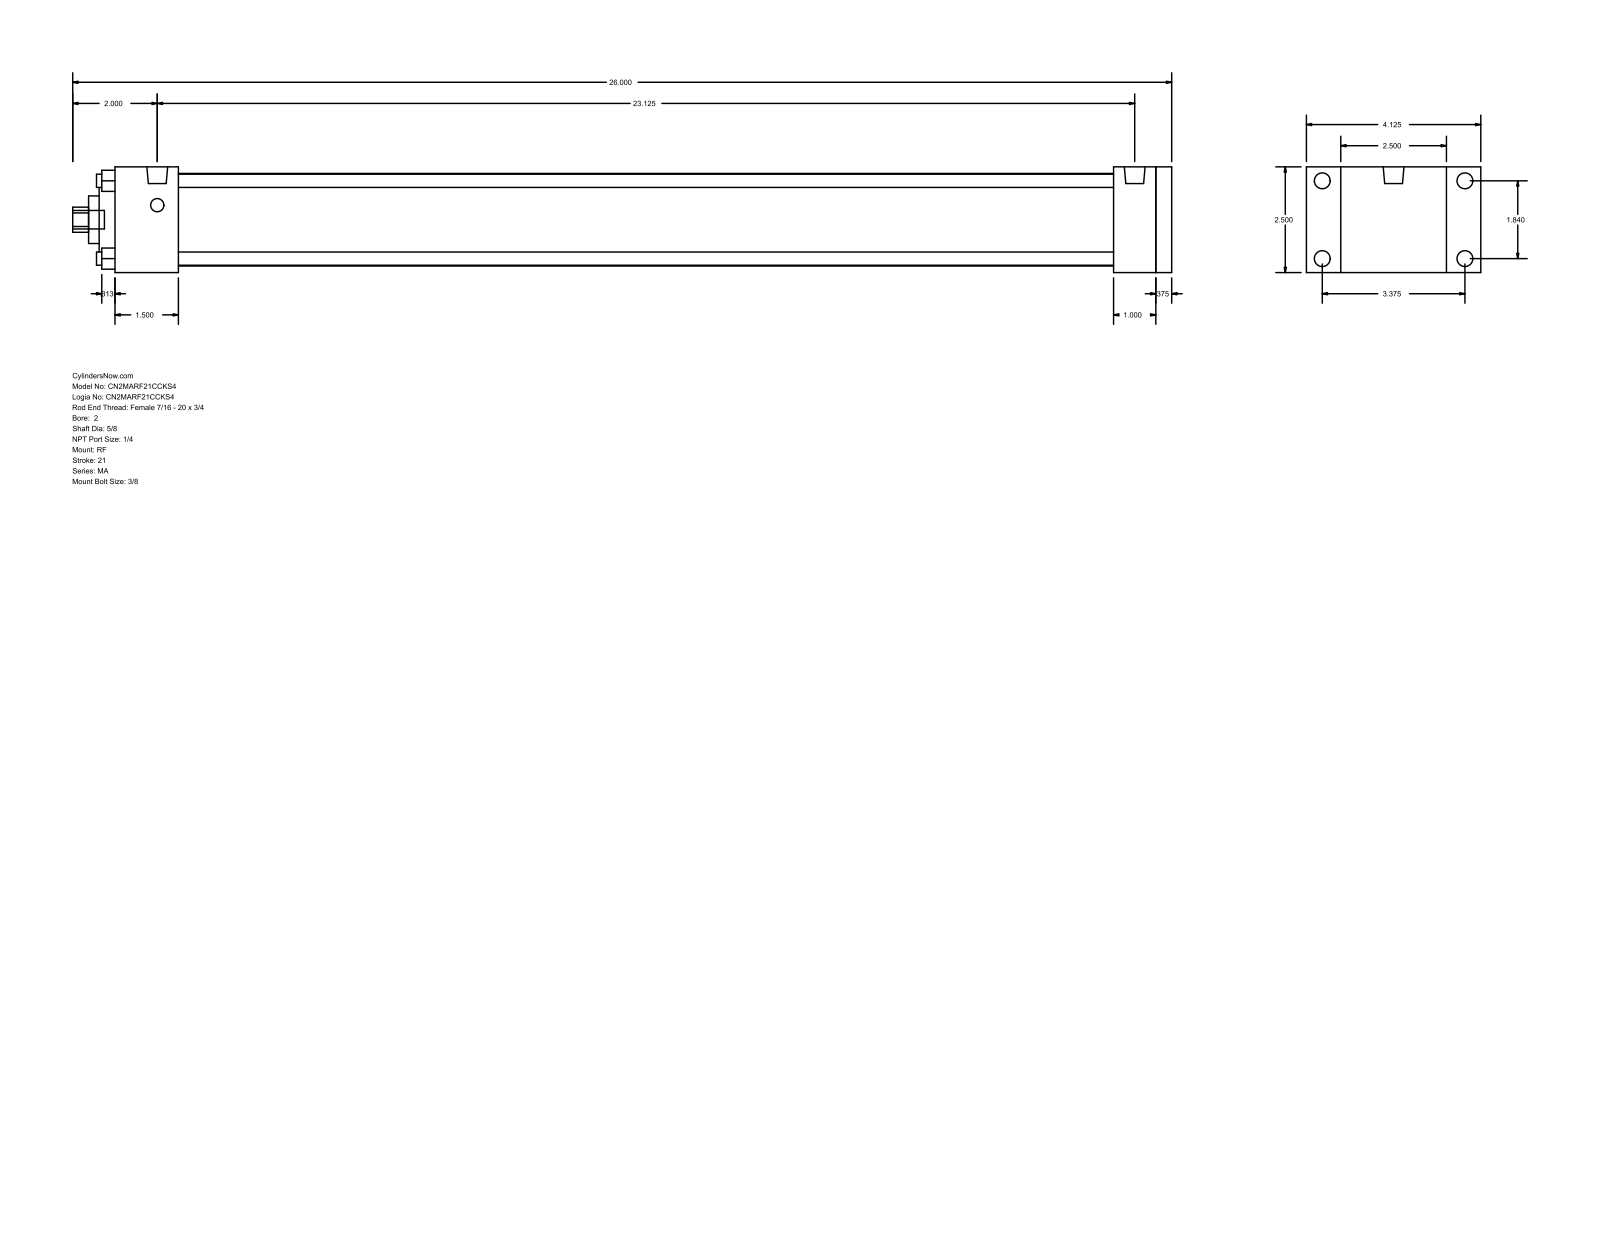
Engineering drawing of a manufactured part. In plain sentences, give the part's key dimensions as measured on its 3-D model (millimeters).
The part is named "MA_RF__0200_0.625". Its 3-D file was written by "GSSL Pune (CONFIG_CONTROL_DESIGN)". It is 0 solids with 94 faces: 65 planar, 29 cylindrical and 0 other. Overall it measures 660.4 by 104.78 by 63.5 millimeters. Round holes: 4 of diameter 7.94, 1 of diameter 15.88, 1 of diameter 28.57, 1 of diameter 50.8, 1 of diameter 55.63. Round bosses or shafts: 4 of diameter 9.53, 4 of diameter 7.94, 2 of diameter 12.49, 1 of diameter 11.11. Partial cylindrical surfaces (rounded edges, fillets, slot ends): 1 of radius 7.54. The main face-to-face distances are 63.5, 9.52, 635, 25.4, 38.1, 625.48, 587.38, 596.9, 600.08, 561.98. The hole center spacings are 33.05, 46.74, 66.1.
